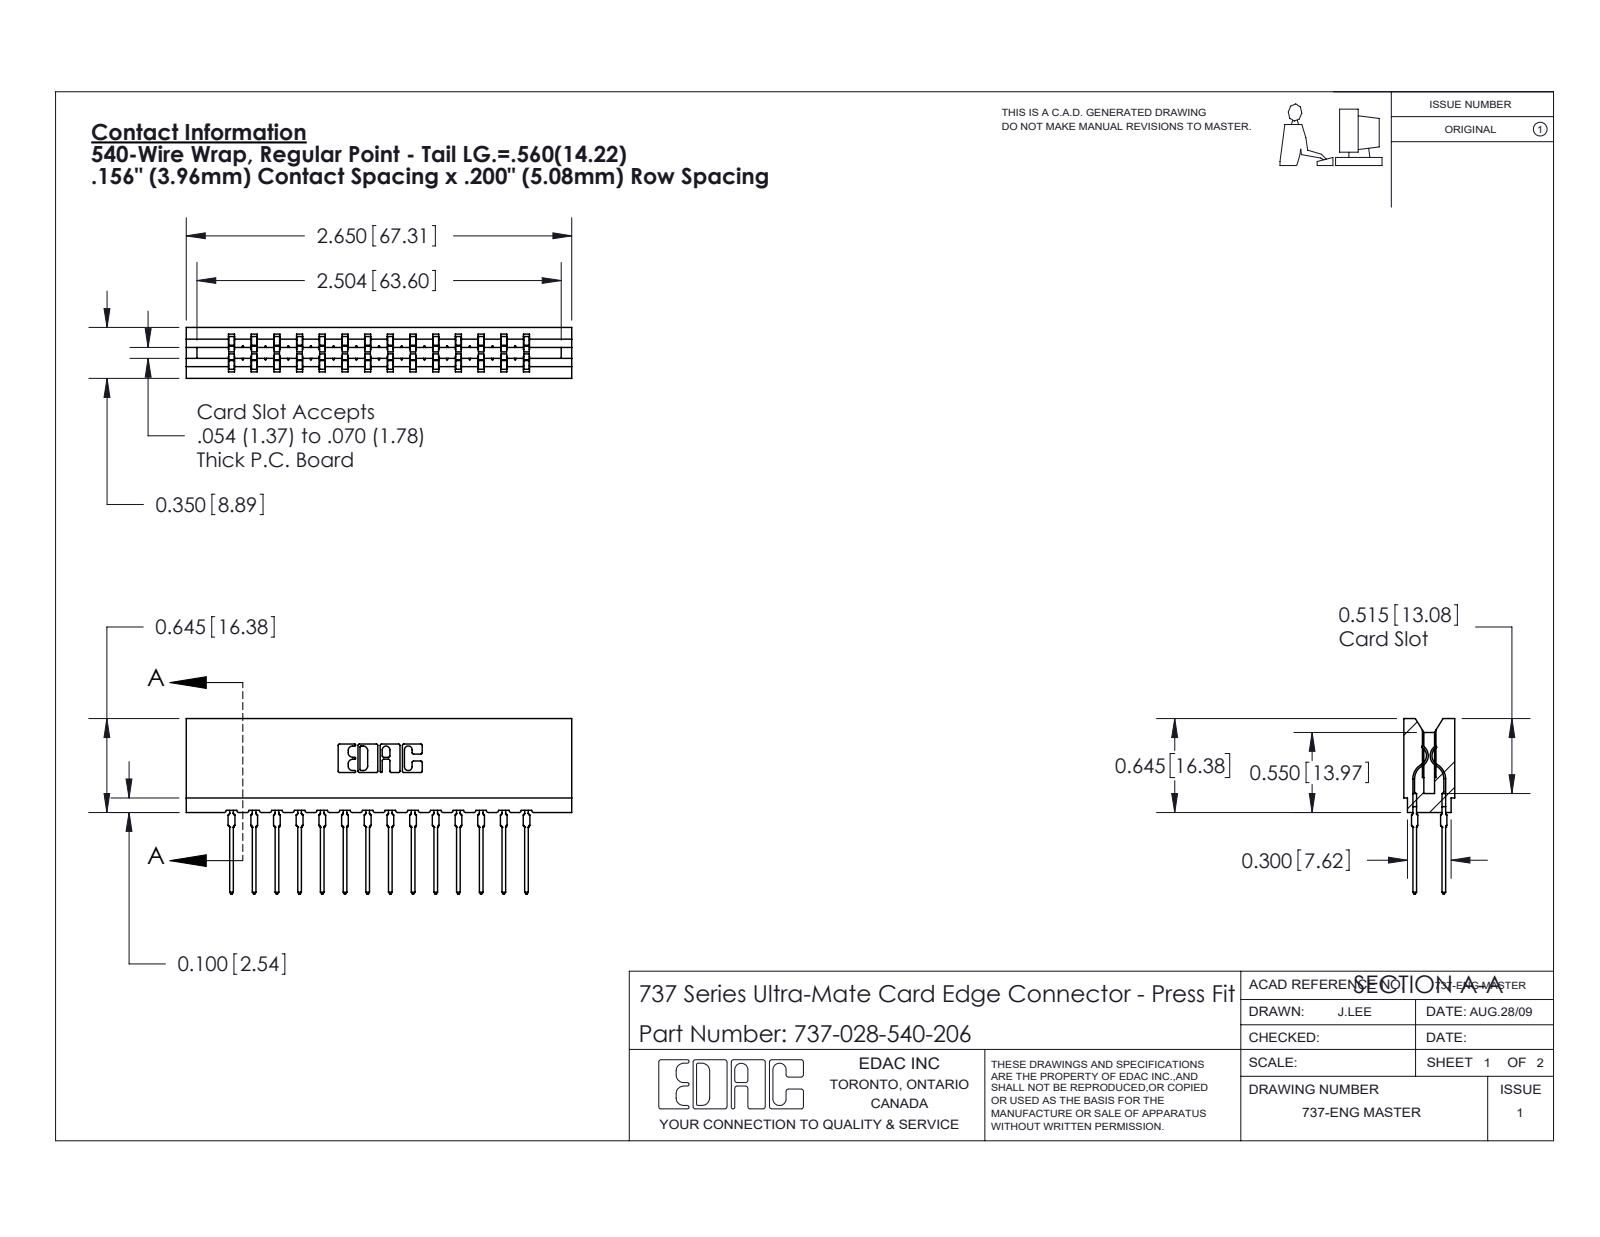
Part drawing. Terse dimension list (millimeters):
name: 737-028-540-206; 745-292-001_540; 737 Part_Insulator Option - 06
written by: SolidWorks 2020 (CONFIG_CONTROL_DESIGN)
unit: mm
bodies: 29 solids, 2615 faces (1357 planar, 530 cylindrical, 728 other)
size: 67.3 × 30.6 × 8.9
volume: 6 900 mm³; area: 9 774 mm²
rounds: 56× R0.5, 28× R0.4, 22× R0.3, 8× R0.1, 8× R0.3, 6× R0.2, 6× R0.8, 3× R0.7
face distances: 3.5, 5.4, 8.9, 4, 15.8, 1.6, 7.3, 1.9, 3.8, 11.9
